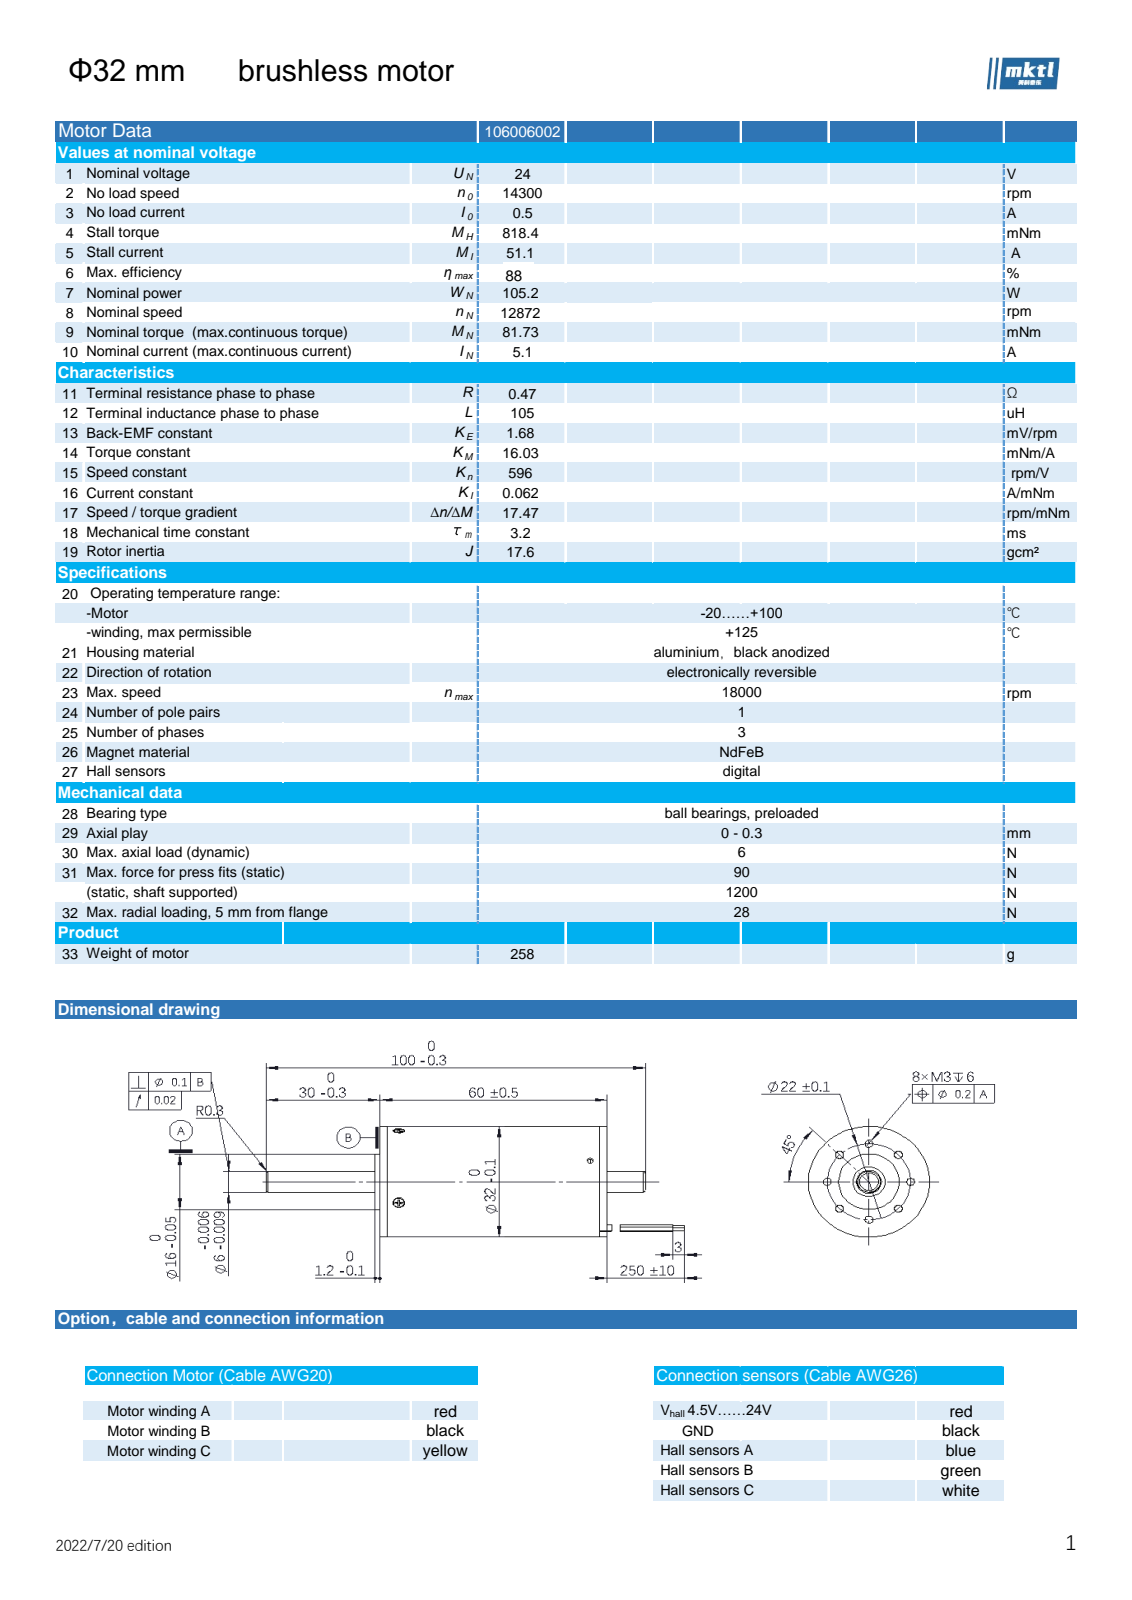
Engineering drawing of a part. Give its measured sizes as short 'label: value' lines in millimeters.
name: 106006002
written by: SolidWorks 2025 (AUTOMOTIVE_DESIGN)
unit: mm
bodies: 263 solids, 2549 faces (931 planar, 1513 cylindrical, 105 other)
size: 111.68 × 32 × 32
volume: 41 931 mm³; area: 148 733 mm²
holes: 11× ⌀2.1, 5× ⌀1.1, 5× ⌀1.5, 4× ⌀0.5, 4× ⌀1.25, 4× ⌀3.1, 3× ⌀1.2, 3× ⌀3, 2× ⌀1.6, 1× ⌀1.3, 1× ⌀6, 1× ⌀9
bosses: 7× ⌀1.4, 5× ⌀1.2, 5× ⌀0.8, 4× ⌀2.8, 4× ⌀1.6, 4× ⌀1.3, 3× ⌀4, 3× ⌀1.8
rounds: 24× R0.1, 21× R0.3, 11× R0.75, 5× R0.2, 4× R1.5, 2× R8, 1× R6, 1× R7.5
face distances: 0.6, 0.4, 0.8, 1, 1.2, 1.4, 1.6, 1.8, 37, 2
hole spacings: 8.42, 11, 15.56, 20.33, 2, 12.25, 22.7, 23.62
